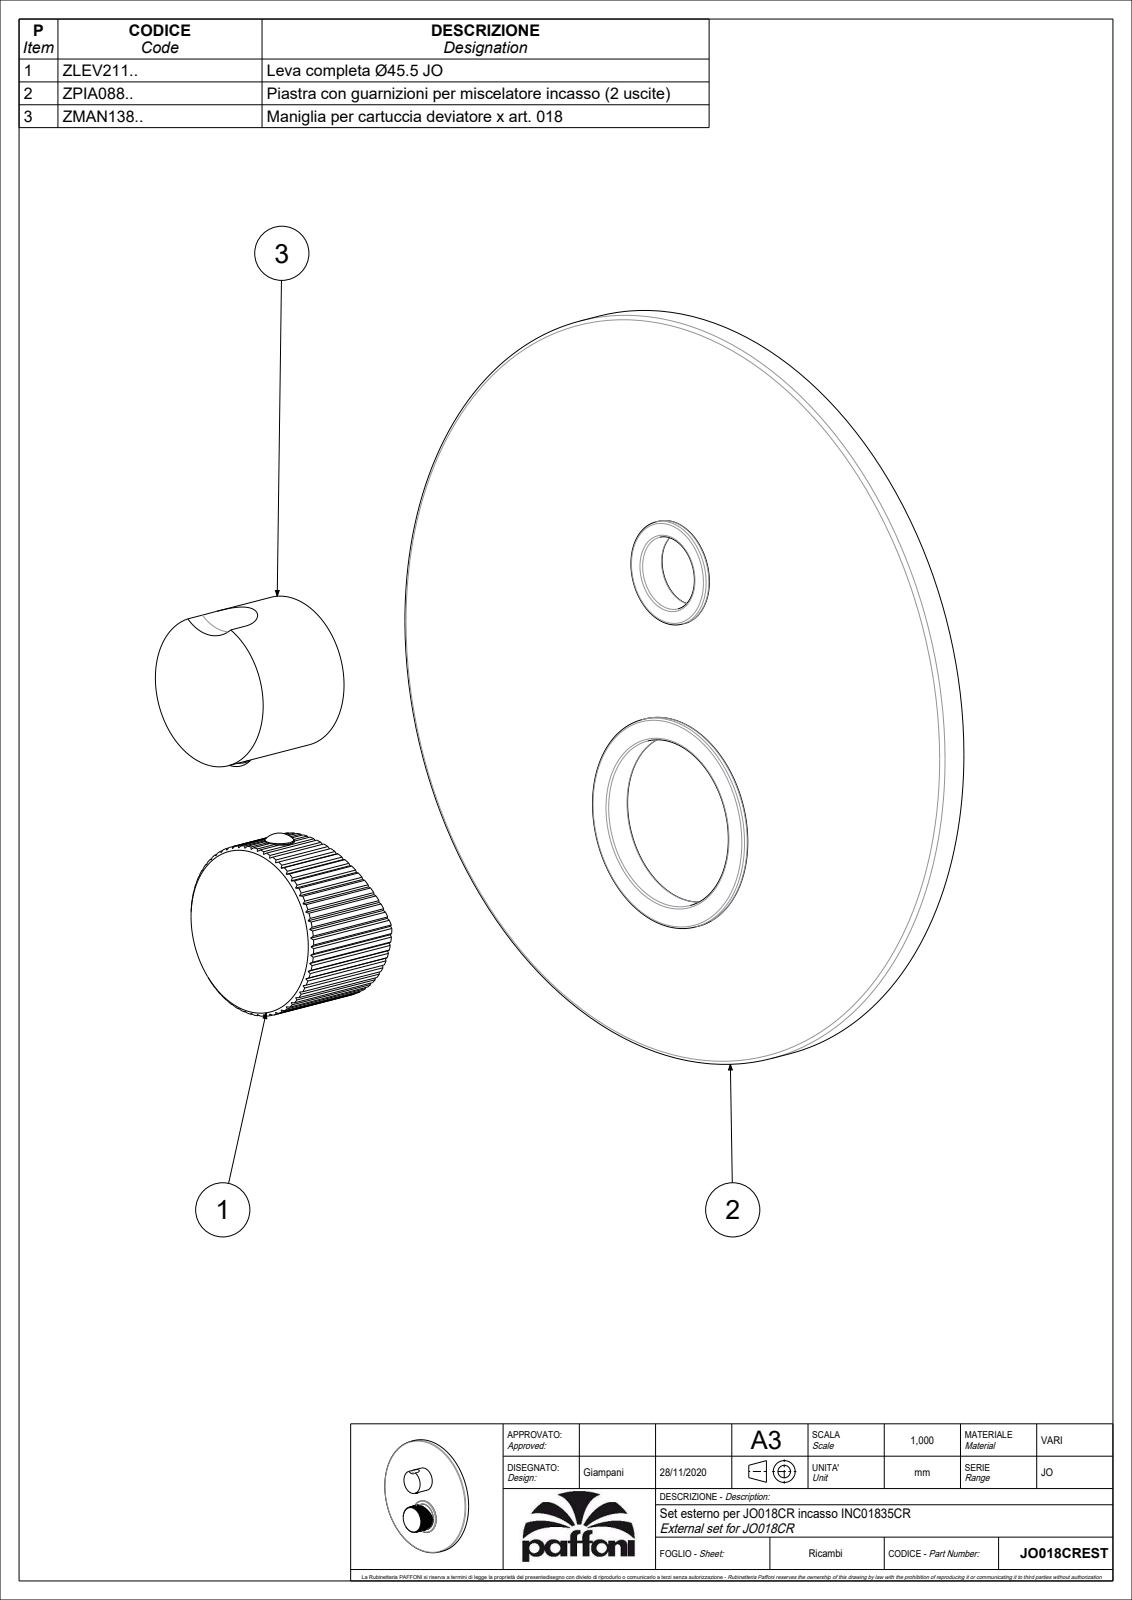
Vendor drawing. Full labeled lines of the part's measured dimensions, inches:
Part name (STEP PRODUCT): JO018CREST
STEP written by: CREO PARAMETRIC BY PTC INC, 2020044 (CONFIG_CONTROL_DESIGN)
Units: inches
Bodies: 3 solids, 459 faces (231 planar, 158 cylindrical, 70 other)
Overall size (bounding box): 7.874 × 7.874 × 1.63
Volume: 11.04 in³ · Surface area: 158.1 in²
Round holes (diameter × count): ⌀0.118 ×2, ⌀0.126 ×1, ⌀0.165 ×1, ⌀0.413 ×1, ⌀0.583 ×1, ⌀0.752 ×1, ⌀1.417 ×1, ⌀1.654 ×1, ⌀1.756 ×1, ⌀1.969 ×1, ⌀5.709 ×1, ⌀7.795 ×1
Round bosses / shafts (diameter × count): ⌀0.299 ×2, ⌀0.217 ×2, ⌀0.197 ×2, ⌀7.874 ×1, ⌀7.677 ×1, ⌀2.213 ×1, ⌀1.965 ×1, ⌀1.575 ×1
Partial cylindrical surfaces — rounded edges, fillets, slot ends (radius × count): R0.157 ×1, R0.492 ×1, R0.896 ×1
Main face-to-face distances: 0.039, 0.315, 0.354, 0.079, 0.433, 1.063, 1.181, 1.142, 0.118, 1.496
Hole centre spacings: 0.039, 0.394, 1.268, 1.409, 1.661, 2.677, 3.071
